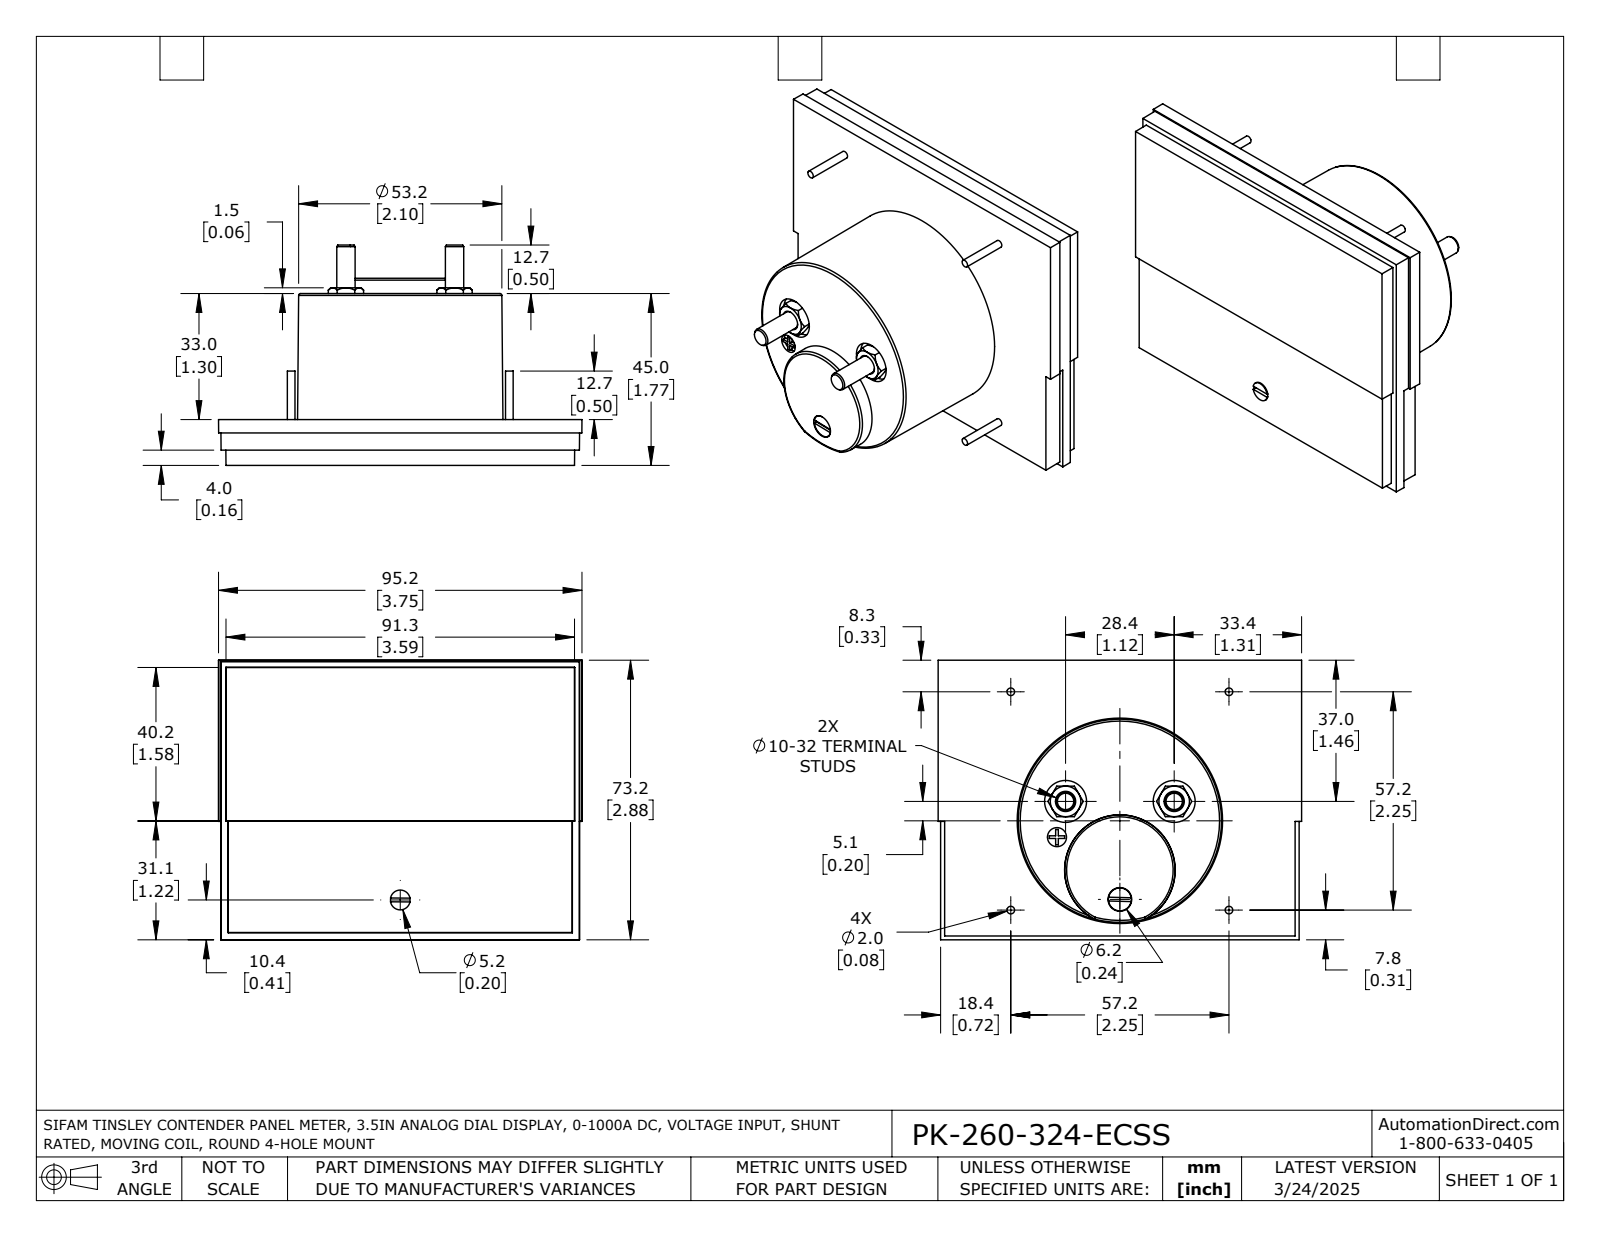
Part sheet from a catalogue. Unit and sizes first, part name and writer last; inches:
Units: inches
Overall size (bounding box): 3.748 × 2.882 × 2.272
Round holes (diameter × count): ⌀0.433 ×2, ⌀0.197 ×1, ⌀0.244 ×1
Round bosses / shafts (diameter × count): ⌀0.079 ×4, ⌀0.189 ×2, ⌀0.236 ×1, ⌀0.205 ×1
Partial cylindrical surfaces — rounded edges, fillets, slot ends (radius × count): R0.1 ×1
Main face-to-face distances: 0.472, 0.03, 0.443, 1.772, 1.299, 1.742, 0.157, 0.073, 0.315, 1.457
Hole centre spacings: 1.155, 0.379, 0.912, 1.12, 1.263
Volume: 9.446 in³ · Surface area: 38.39 in²
Bodies: 1 solid, 163 faces (76 planar, 31 cylindrical, 56 other)
Part name (STEP PRODUCT): PK-260-324-ECSS
STEP written by: SolidWorks 2021 (AUTOMOTIVE_DESIGN)
